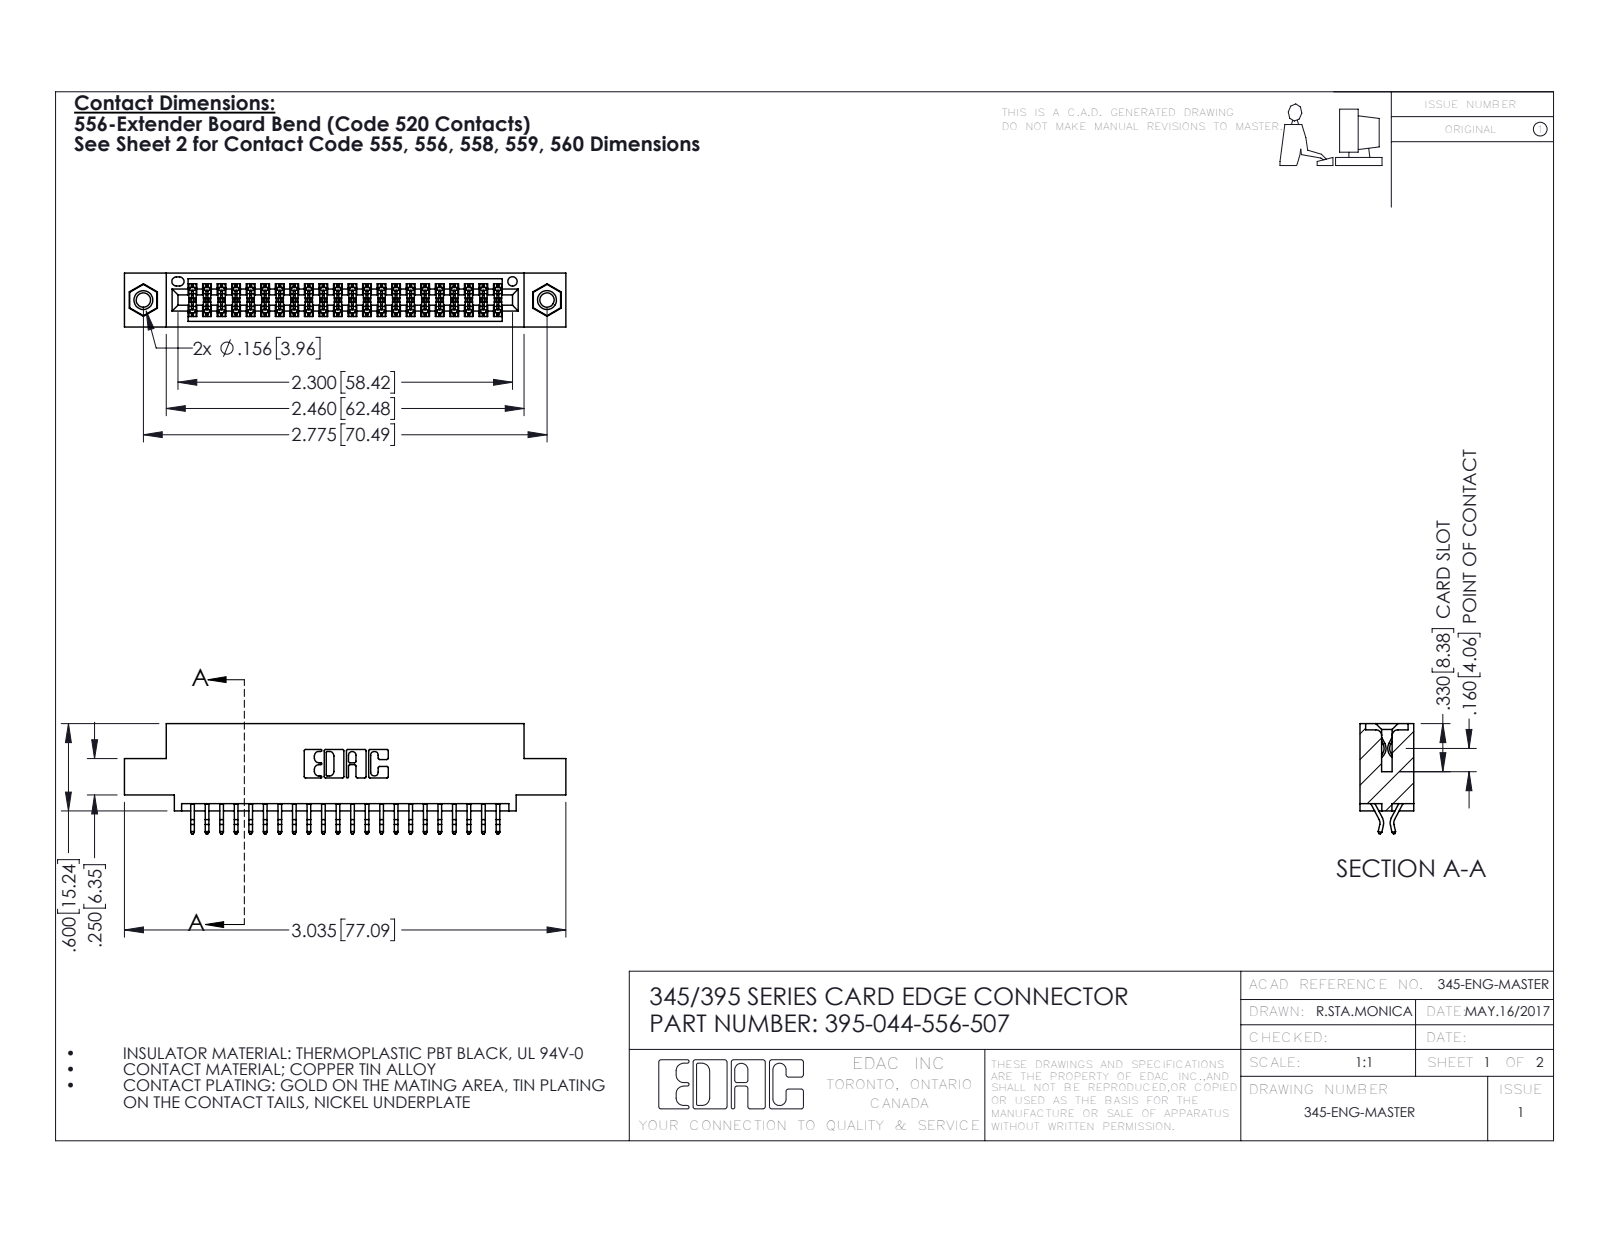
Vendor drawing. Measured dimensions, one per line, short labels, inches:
name: 395-044-556-507; 345-250-001_345-250-005-103; 345 Part_0.110 Offset - 0.156 Dia-TI; 345-292-001_556 Tail
written by: SolidWorks 2016 (CONFIG_CONTROL_DESIGN)
unit: in
bodies: 47 solids, 2654 faces (1744 planar, 894 cylindrical, 16 other)
size: 3.035 × 0.757 × 0.37
volume: 0.44 in³; area: 16.06 in²
holes: 2× ⌀0.098, 2× ⌀0.125, 2× ⌀0.156, 1× ⌀0.064
bosses: 2× ⌀0.155
rounds: 66× R0.006, 22× R0.01, 6× R0.007, 6× R0.031, 3× R0.026, 2× R0.01, 2× R0.014, 2× R0.019
face distances: 0.072, 0.298, 0.37, 0.2, 0.025, 0.098, 0.272, 0.225, 0.175, 0.149
hole spacings: 0.27, 2.541, 2.775
